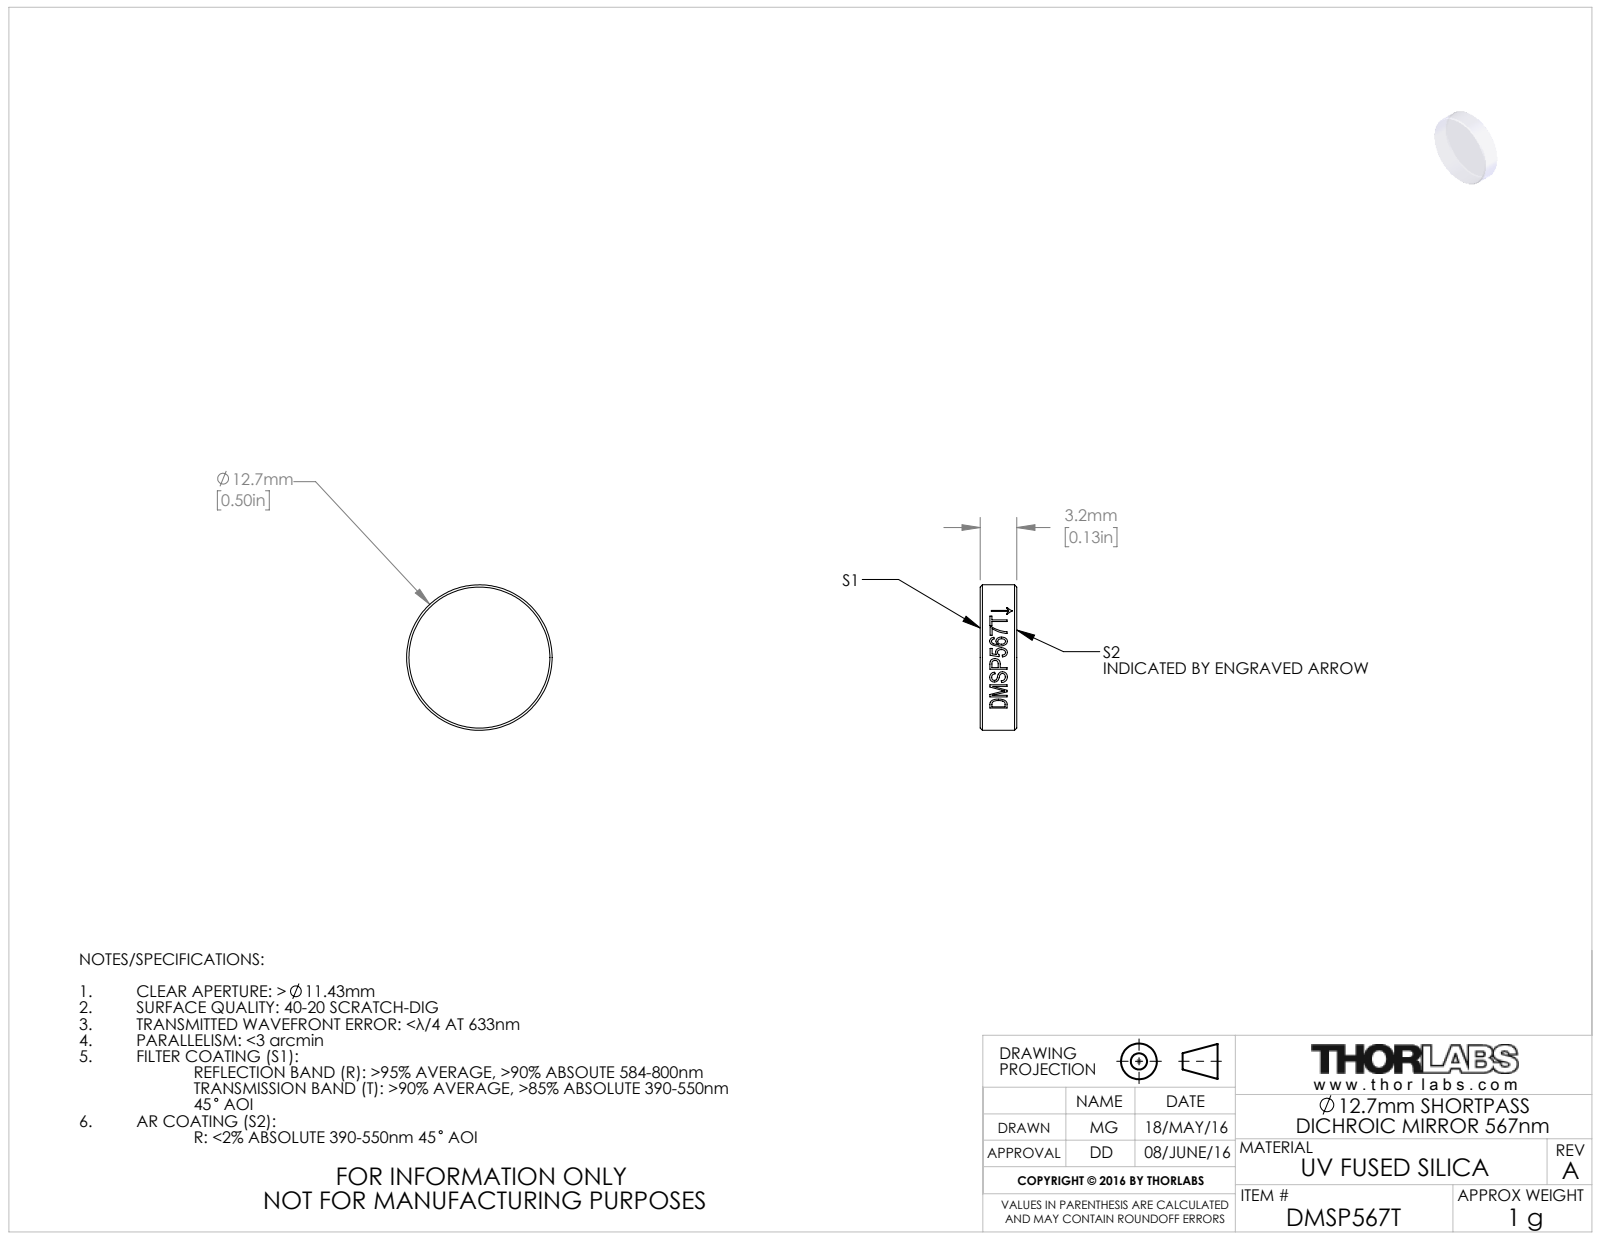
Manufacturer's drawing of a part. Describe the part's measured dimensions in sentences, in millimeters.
The part is named "TTN045274-E0W". Its 3-D file was written by "SolidWorks 2016 (CONFIG_CONTROL_DESIGN)". It is 1 solid with 20 faces: 2 planar, 14 cylindrical and 4 other. Overall it measures 12.7 by 12.7 by 3.2 millimeters. Its volume is 404 cubic millimeters and its surface area 372 square millimeters. Round bosses or shafts: 1 of diameter 12.7. The main face-to-face distances are 3.2.
